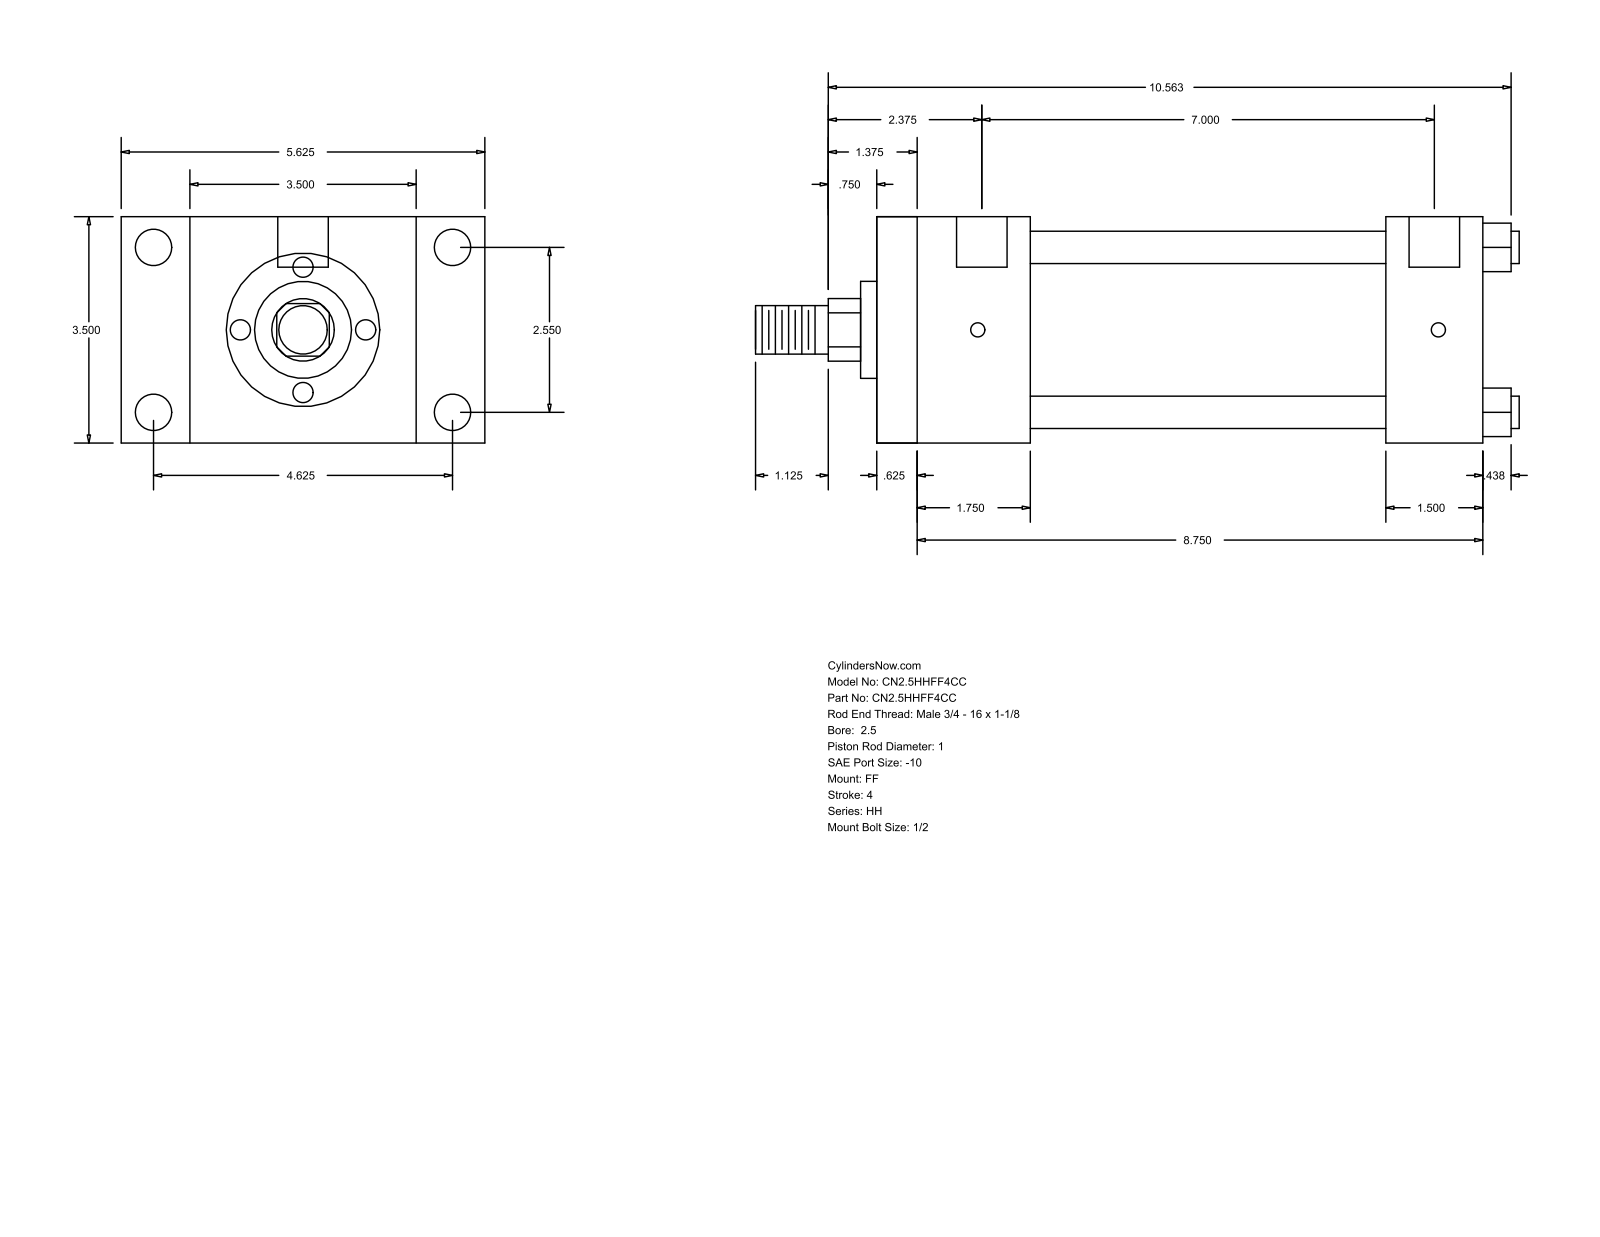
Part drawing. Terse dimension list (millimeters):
name: HH_FF__0250_1
written by: GSSL Pune (CONFIG_CONTROL_DESIGN)
unit: mm
bodies: 0 solids, 92 faces (64 planar, 28 cylindrical, 0 other)
size: 300.04 × 142.88 × 88.9
holes: 4× ⌀5.56, 4× ⌀14.3, 2× ⌀19.84
bosses: 4× ⌀12.7, 1× ⌀73.03, 1× ⌀38.1, 1× ⌀25.4, 1× ⌀19.05
rounds: 1× R12.29
face distances: 88.9, 238.13, 15.87, 222.26, 60.33, 44.46, 177.8, 200.02, 184.15, 139.69
hole spacings: 1.59, 64.76, 117.48, 134.15, 179.38, 180.97, 177.79
